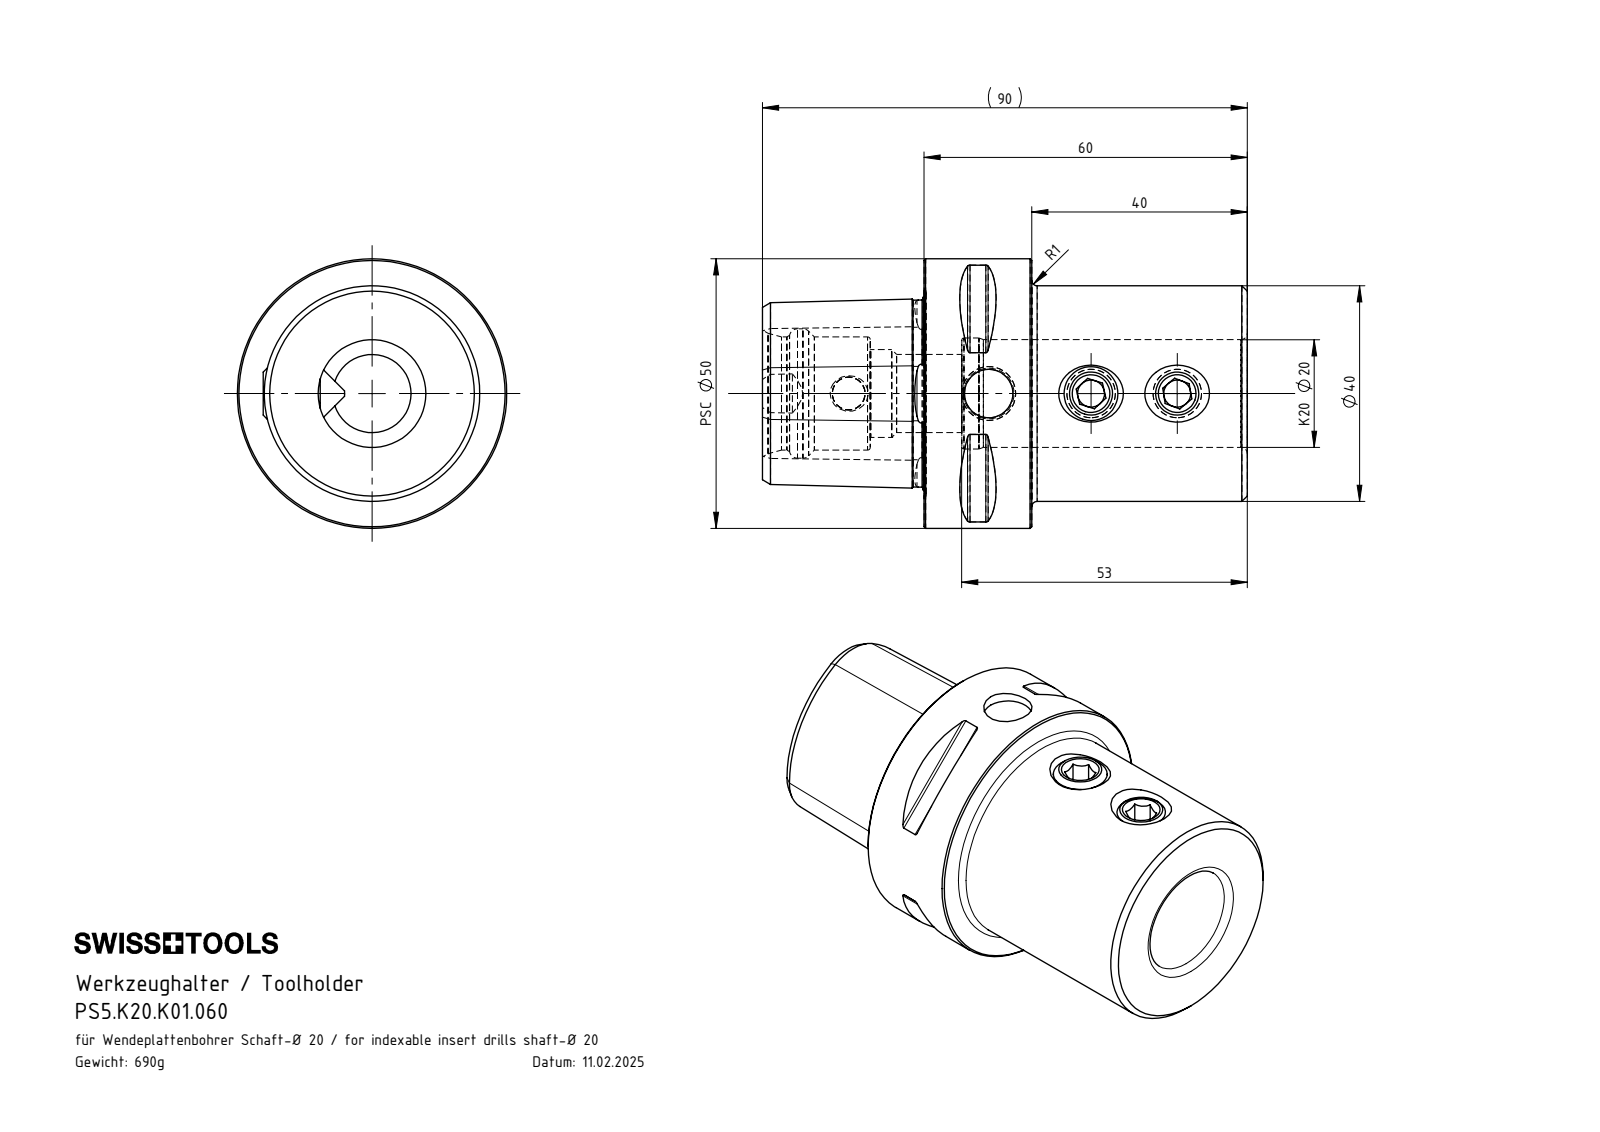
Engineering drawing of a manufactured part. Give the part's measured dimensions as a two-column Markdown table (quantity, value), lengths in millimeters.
| quantity | value |
| --- | --- |
| part name | PS5.K20.K01.060; K20-ER2.010.014_PreviewCfg; PS5-K20.K01.060_A; K20-ER1.010.012_PreviewCfg |
| STEP written by | SolidWorks 2022 (AUTOMOTIVE_DESIGN) |
| units | millimeters |
| bodies | 3 solids, 206 faces (50 planar, 47 cylindrical, 109 other) |
| overall size | 90 × 50 × 50 |
| volume | 87 852 mm³ |
| surface area | 22 208 mm² |
| round holes (diameter × count) | 9 × 3, 5 × 2, 6.1 × 1, 10 × 1, 14.5 × 1, 16.3 × 1, 20 × 1, 20.6 × 1, 21 × 1, 24 × 1 |
| round bosses / shafts (diameter × count) | 10 × 2, 50 × 1, 40 × 1 |
| partial cylindrical surfaces (radius × count) | 0.5 × 8, 5 × 1 |
| main face-to-face distances | 60, 20, 40, 30, 50, 90, 19.18, 7, 37, 13 |
| hole center spacings | 16, 19, 26, 35, 45, 61 |
